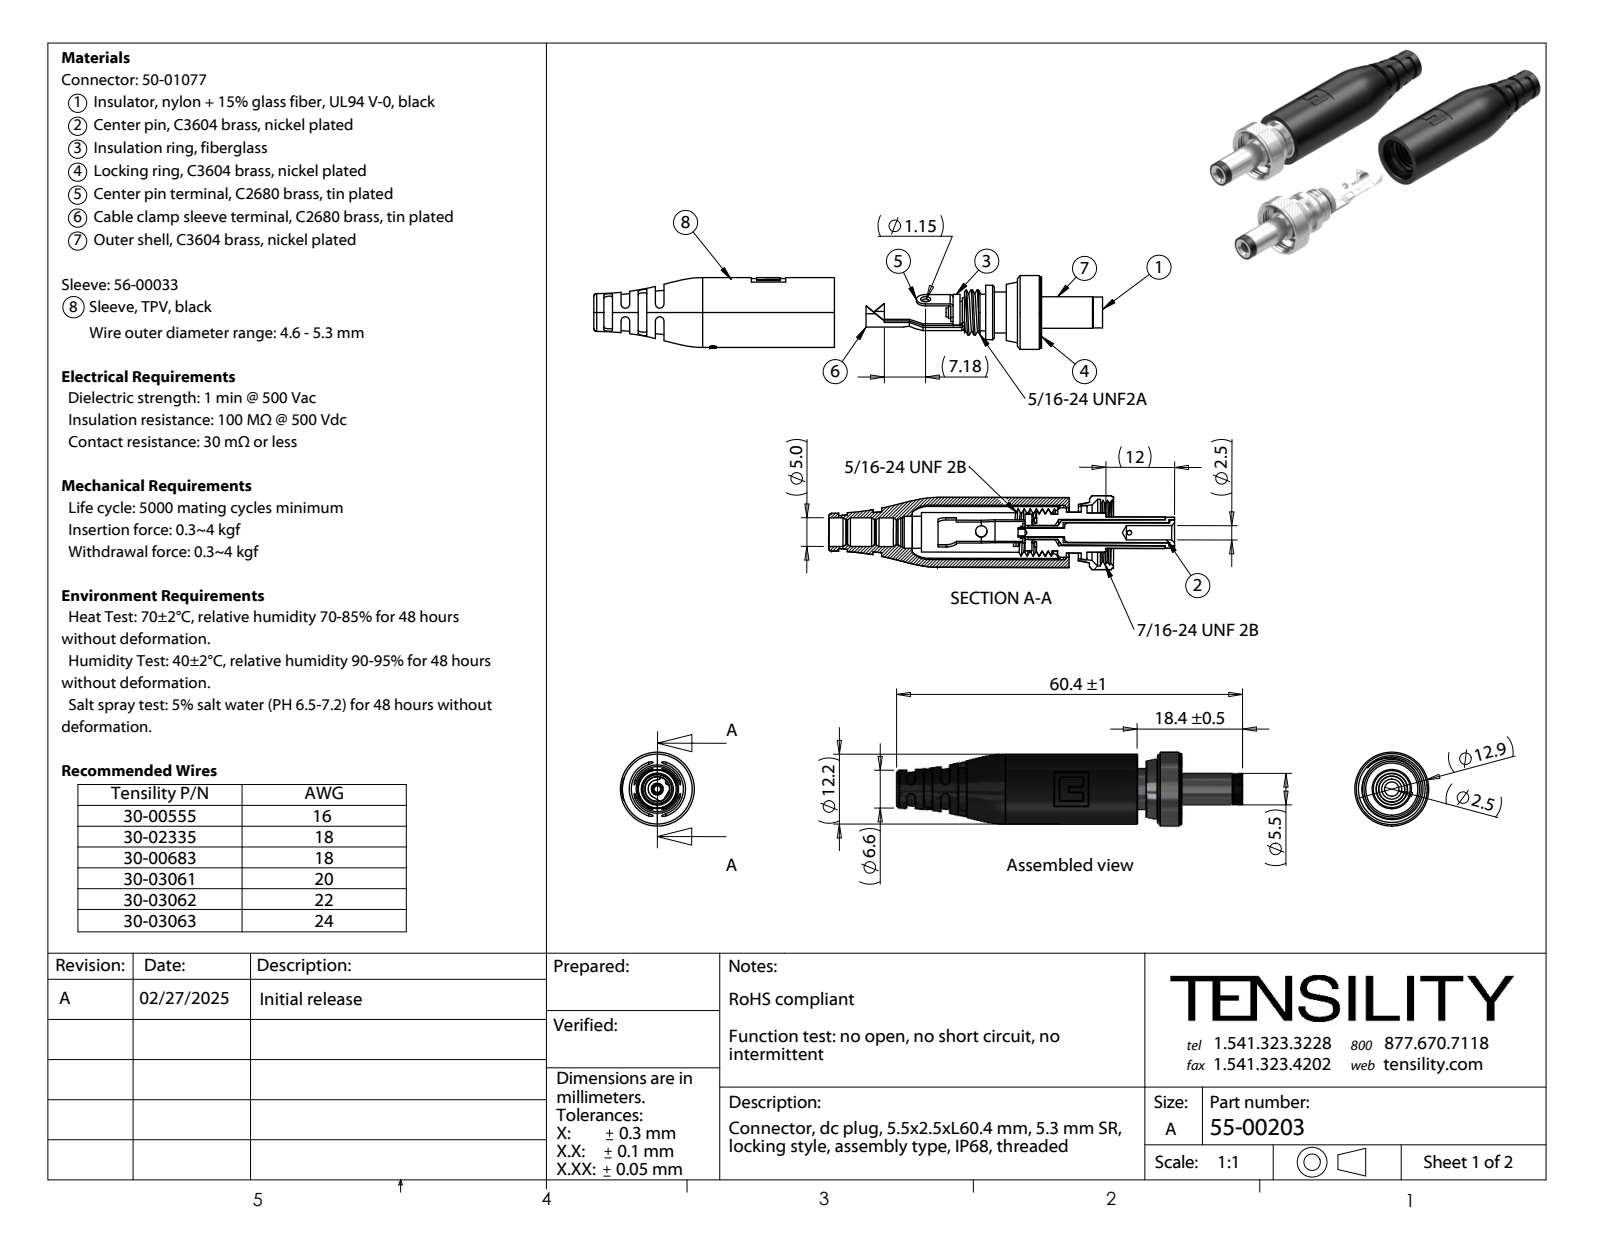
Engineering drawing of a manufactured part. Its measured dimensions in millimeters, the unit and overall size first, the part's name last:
Units: millimetres
Overall size (bounding box): 60.95 × 12.9 × 12.9
Round holes (diameter × count): ⌀1.15 ×2, ⌀0.8 ×1, ⌀1.6 ×1, ⌀2 ×1, ⌀2.45 ×1, ⌀2.5 ×1, ⌀3.35 ×1, ⌀3.55 ×1, ⌀4.55 ×1, ⌀4.6 ×1, ⌀5.6 ×1, ⌀6.9 ×1
Round bosses / shafts (diameter × count): ⌀12.9 ×1, ⌀12.4 ×1, ⌀12.2 ×1, ⌀7.85 ×1, ⌀7.15 ×1, ⌀6.85 ×1, ⌀6.4 ×1, ⌀5.5 ×1
Partial cylindrical surfaces — rounded edges, fillets, slot ends (radius × count): R0.75 ×8, R0.2 ×4, R1.57 ×2, R6.1 ×2, R0.1 ×1, R0.4 ×1, R0.5 ×1, R0.6 ×1
Main face-to-face distances: 4.1, 1.45, 29.8, 0.4, 1.5, 5.55, 5.95, 5.45, 6, 1.6
Volume: 3 421 mm³ · Surface area: 7 113 mm²
Bodies: 9 solids, 400 faces (128 planar, 146 cylindrical, 126 other)
Part name (STEP PRODUCT): 50-01077; 5.0(4.6-5.3); 55-00203; 50-01077_Tip insulator (+8 more)
STEP written by: SolidWorks 2021 (CONFIG_CONTROL_DESIGN)
